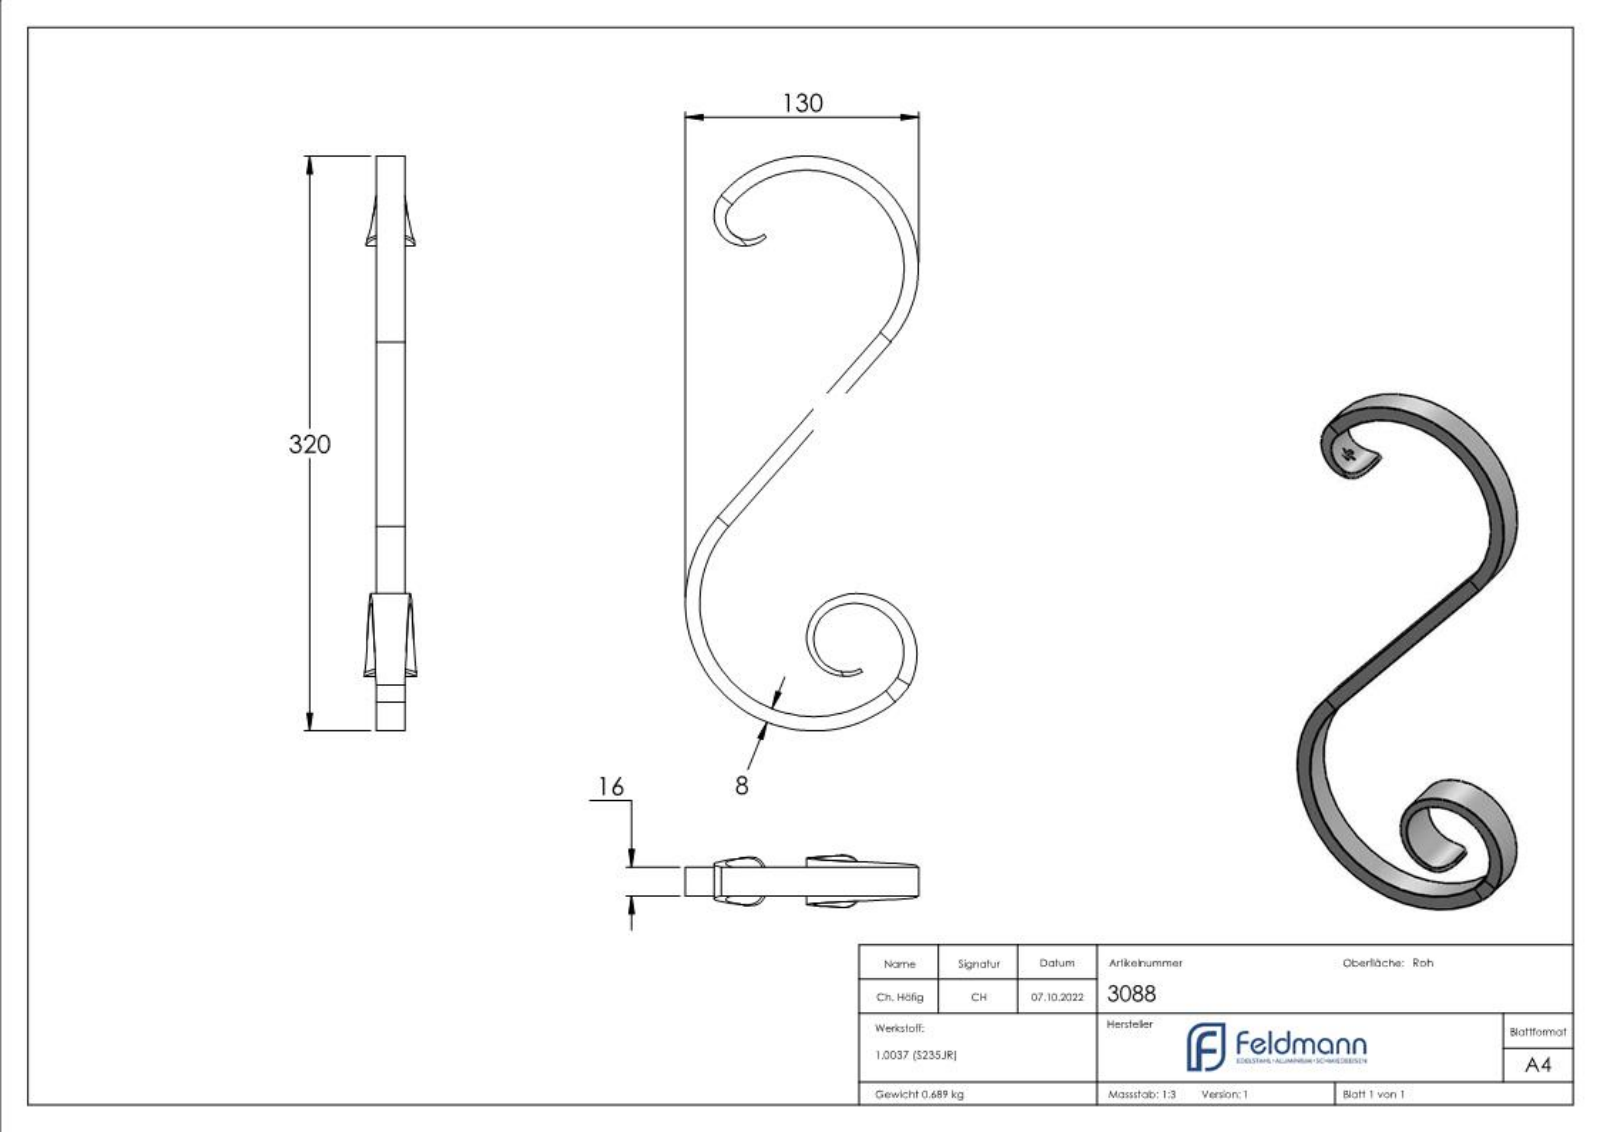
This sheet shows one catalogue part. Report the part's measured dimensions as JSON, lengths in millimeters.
{"part_name": "3088", "step_written_by": "SolidWorks 2018 (CONFIG_CONTROL_DESIGN)", "units": "millimeters", "bodies": {"solids": 1, "faces": 255, "planar": 89, "cylindrical": 8, "other": 158}, "overall_size": [320, 130, 28.93], "volume_mm3": 88307, "surface_area_mm2": 35942, "partial_cylinders_radius": [[28, 1], [36, 1], [54.4, 1], [62.4, 1], [63.54, 1], [71.54, 1]], "face_to_face_distances": [16, 2.21, 1.14, 1.12, 0.34, 0.39, 3.35, 8, 3.15, 2.02]}
